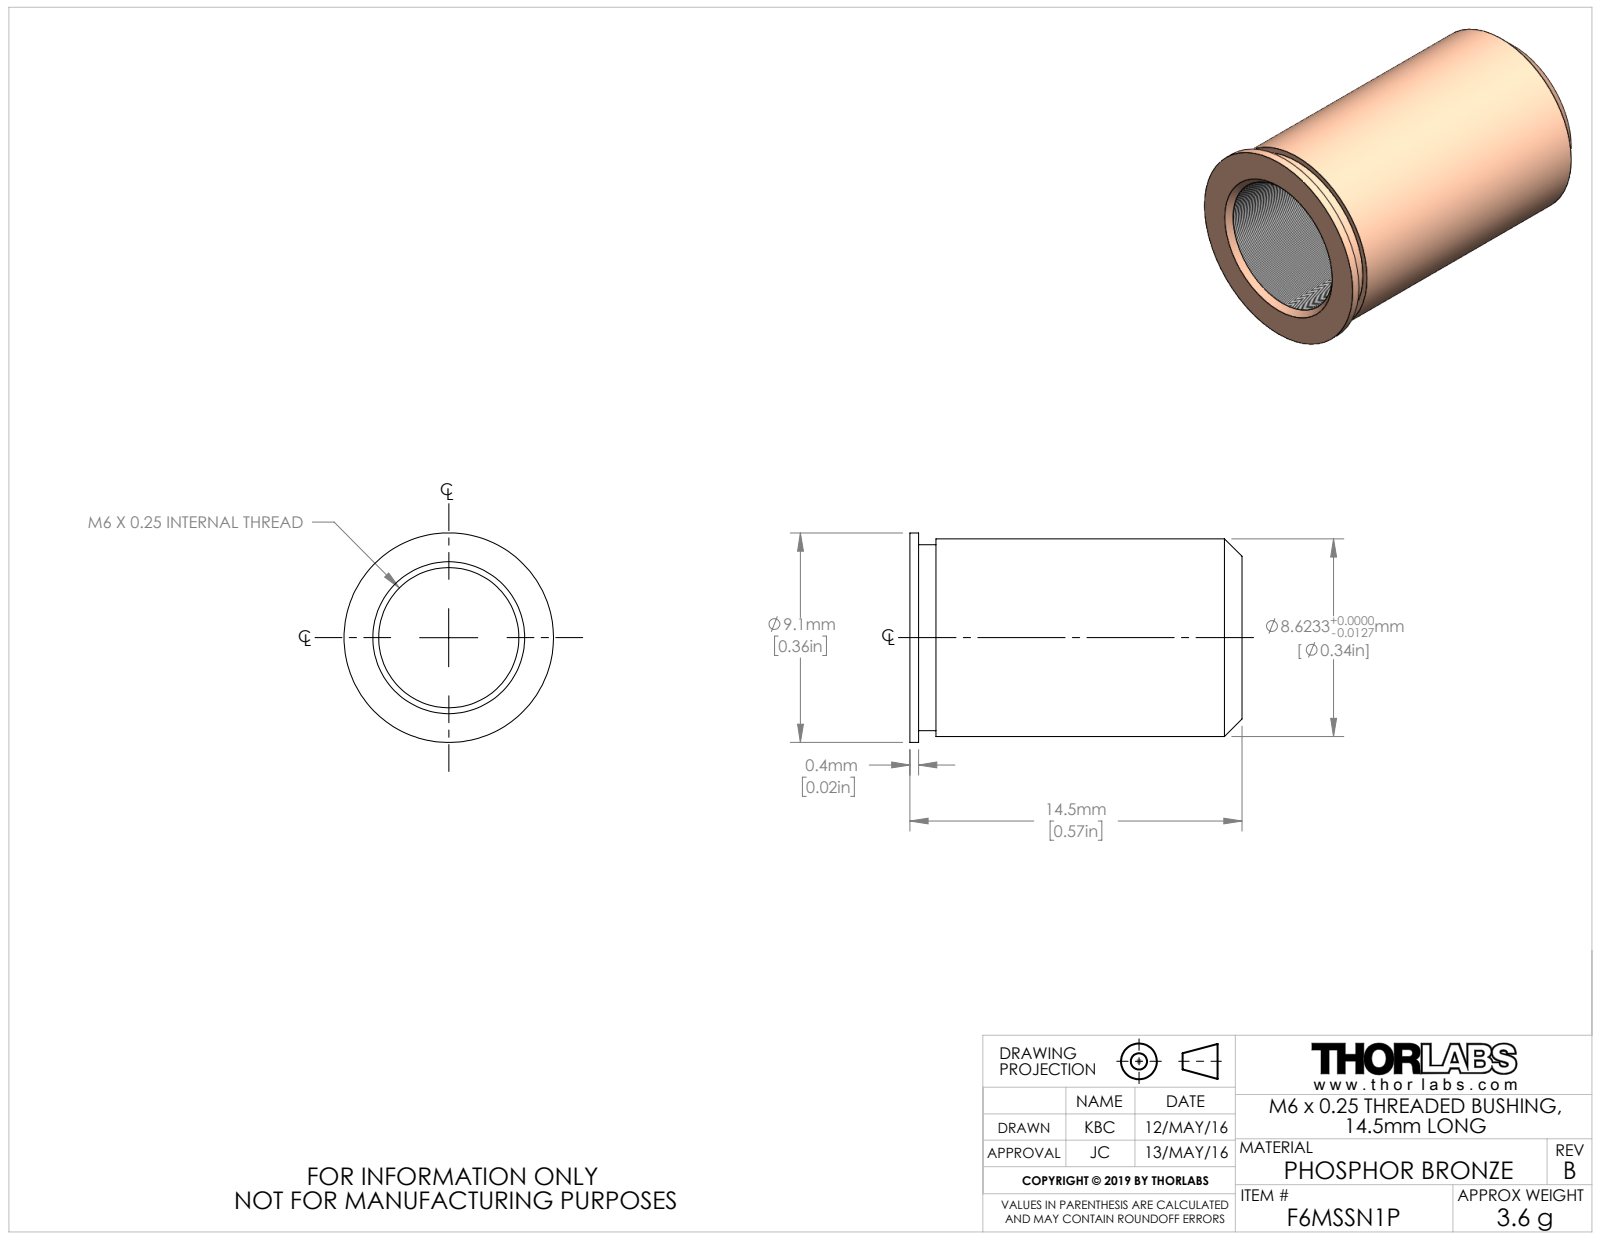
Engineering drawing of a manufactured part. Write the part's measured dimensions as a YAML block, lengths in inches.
part_name: "TTN102542-E0W"
step_written_by: "SolidWorks 2016 (CONFIG_CONTROL_DESIGN)"
units: inches
bodies: {solids: 1, faces: 18, planar: 4, cylindrical: 8, other: 6}
overall_size: [0.571, 0.36, 0.36]
volume: 0.025
surface_area: 1.14
round_holes:
  - {diameter: 0.241, count: 1}
round_bosses_or_shafts:
  - {diameter: 0.36, count: 1}
  - {diameter: 0.339, count: 1}
  - {diameter: 0.32, count: 1}
face_to_face_distances: [0.015, 0.03, 0.045, 0.526, 0.556, 0.571]
